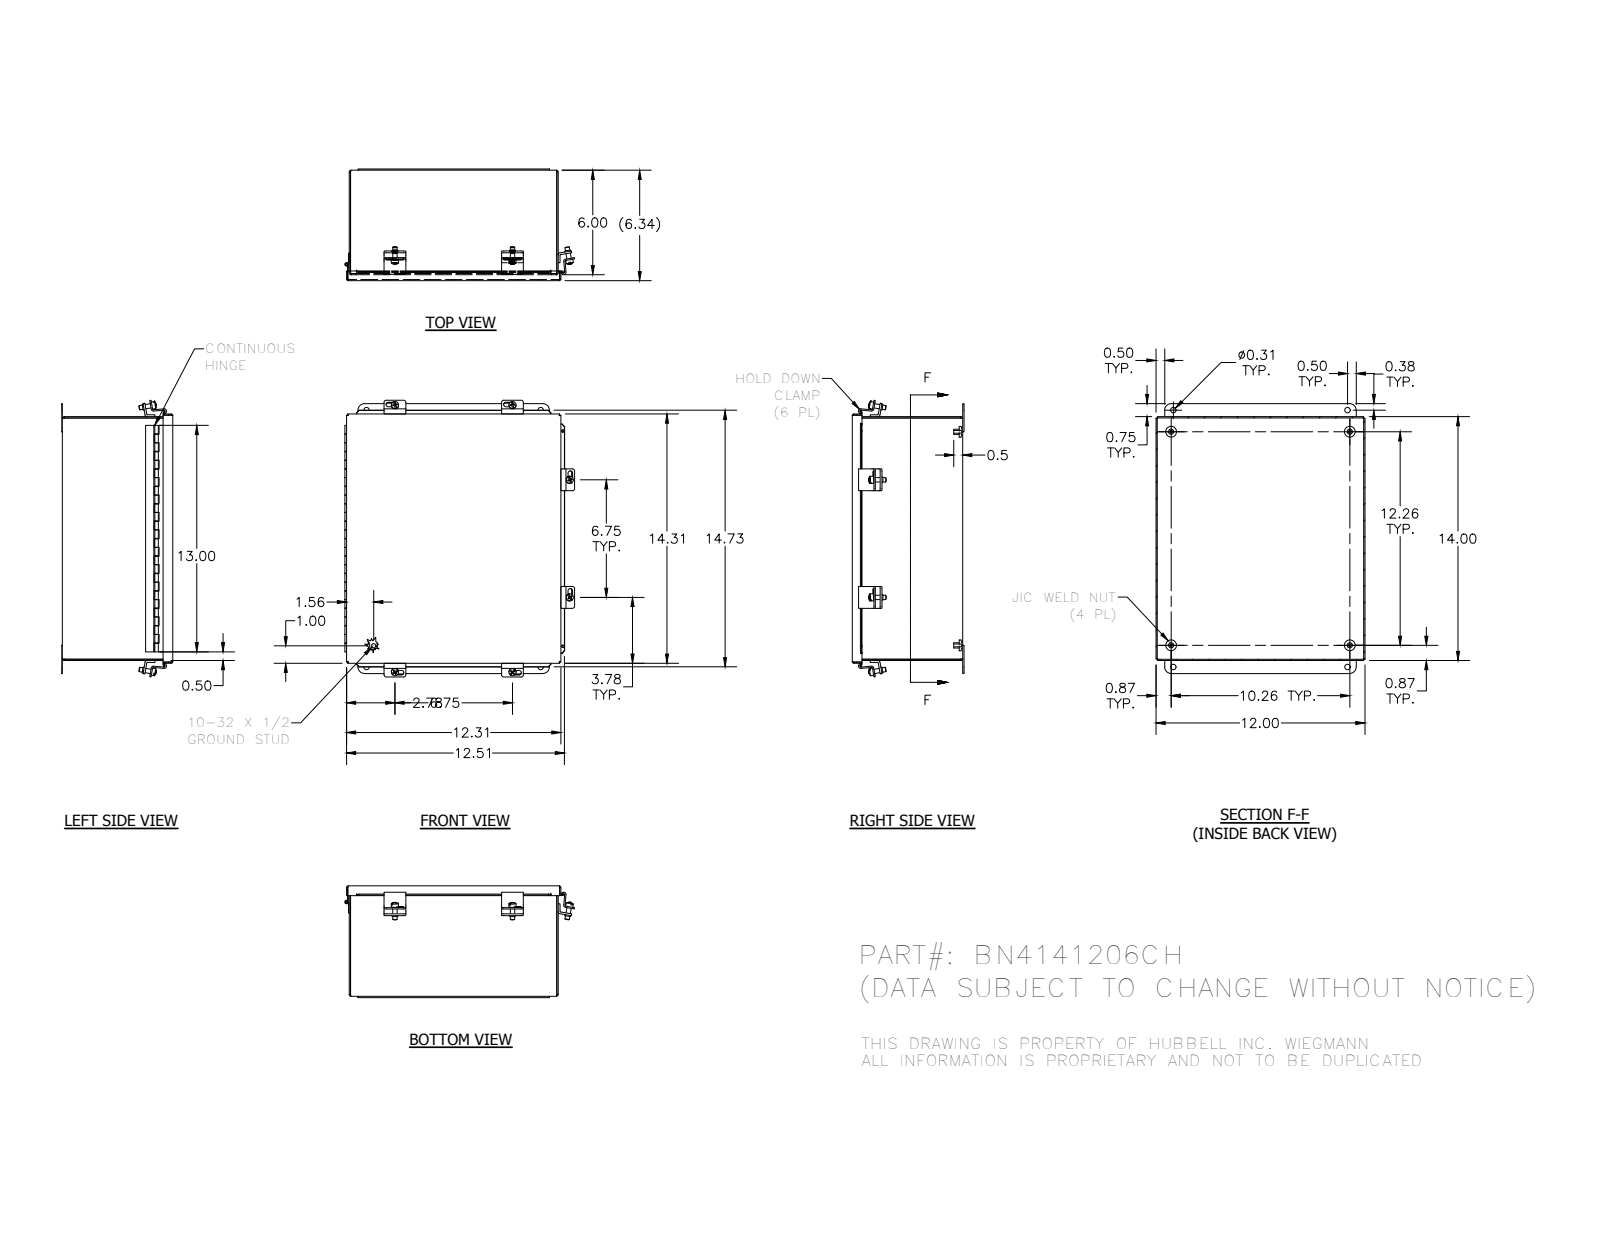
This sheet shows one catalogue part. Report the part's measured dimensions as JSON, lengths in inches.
{"part_name": "B_1412CH_LID; 316168; 38811; 3499 (+8 more)", "step_written_by": "Autodesk Inventor 2016 (AUTOMOTIVE_DESIGN)", "units": "inches", "bodies": {"solids": 20, "faces": 527, "planar": 337, "cylindrical": 139, "other": 51}, "overall_size": [15.5, 13.086, 6.259], "volume_in3": 58.7, "surface_area_in2": 1631, "round_holes": [[0.156, 4], [0.31, 4], [0.14, 2], [0.196, 2], [0.117, 1]], "round_bosses_or_shafts": [[0.625, 4], [0.3, 4], [0.25, 3], [0.409, 2], [0.344, 2], [0.2, 1], [0.19, 1], [0.1, 1]], "partial_cylinders_radius": [[0.047, 8], [0.121, 8], [0.125, 8], [0.078, 4], [0.133, 4], [0.137, 4], [0.375, 4], [0.031, 3]], "face_to_face_distances": [0.074, 6.125, 0.059, 6.184, 6.051, 6.11, 11.926, 13.926, 12, 11.852], "hole_center_spacings": [1.256, 13.5, 10, 10.202, 10.202, 10.25, 12.25, 14.75]}
